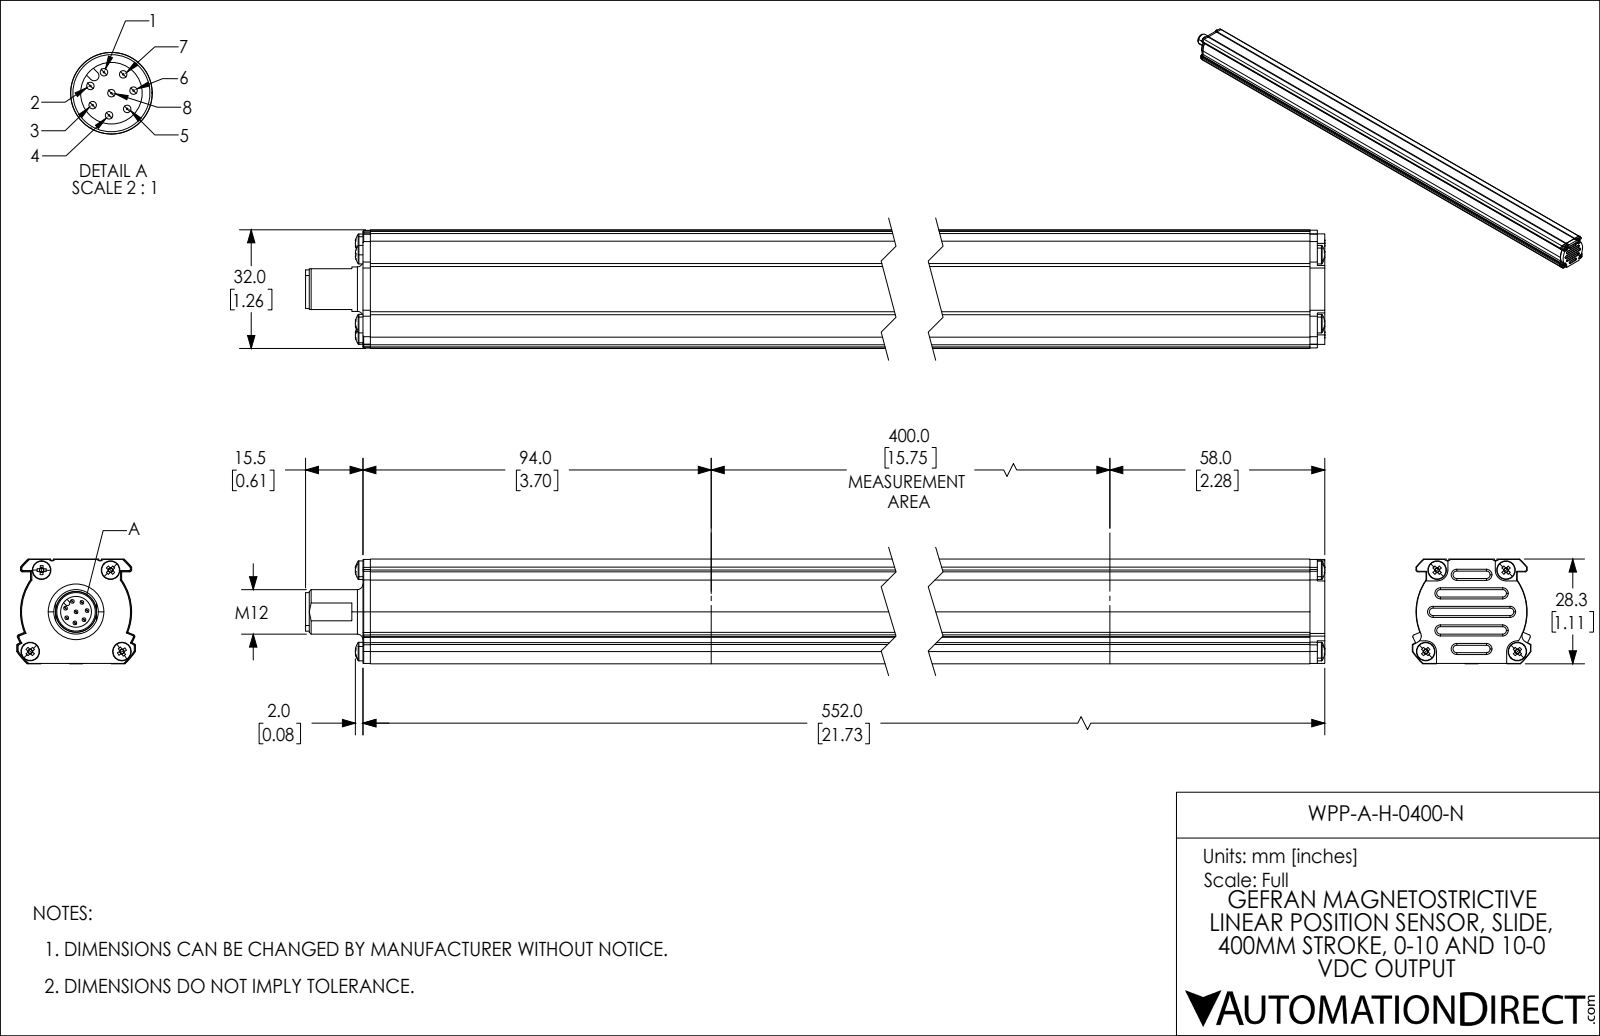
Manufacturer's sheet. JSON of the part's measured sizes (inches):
{"part_name": "WPP-A-H-0400-N", "step_written_by": "SolidWorks 2021 (CONFIG_CONTROL_DESIGN)", "units": "inches", "bodies": {"solids": 20, "faces": 605, "planar": 301, "cylindrical": 131, "other": 173}, "overall_size": [22.344, 1.26, 1.112], "volume_in3": 26.87, "surface_area_in2": 142.3, "round_holes": [[0.102, 5], [0.091, 4], [0.276, 1], [0.327, 1], [0.37, 1]], "round_bosses_or_shafts": [[0.039, 8], [0.197, 4], [0.472, 1], [0.409, 1], [0.376, 1], [0.315, 1]], "partial_cylinders_radius": [[0.02, 8], [0.114, 4], [0.016, 2], [0.039, 2], [0.073, 2], [0.026, 1], [0.079, 1], [0.587, 1]], "face_to_face_distances": [1.102, 1.112, 0.976, 0.967, 0.136, 0.146, 1.114, 21.496, 0.969, 0.079], "hole_center_spacings": [0.644, 0.575, 0.873, 1.215, 0.732, 0.872, 0.974, 0.975]}
